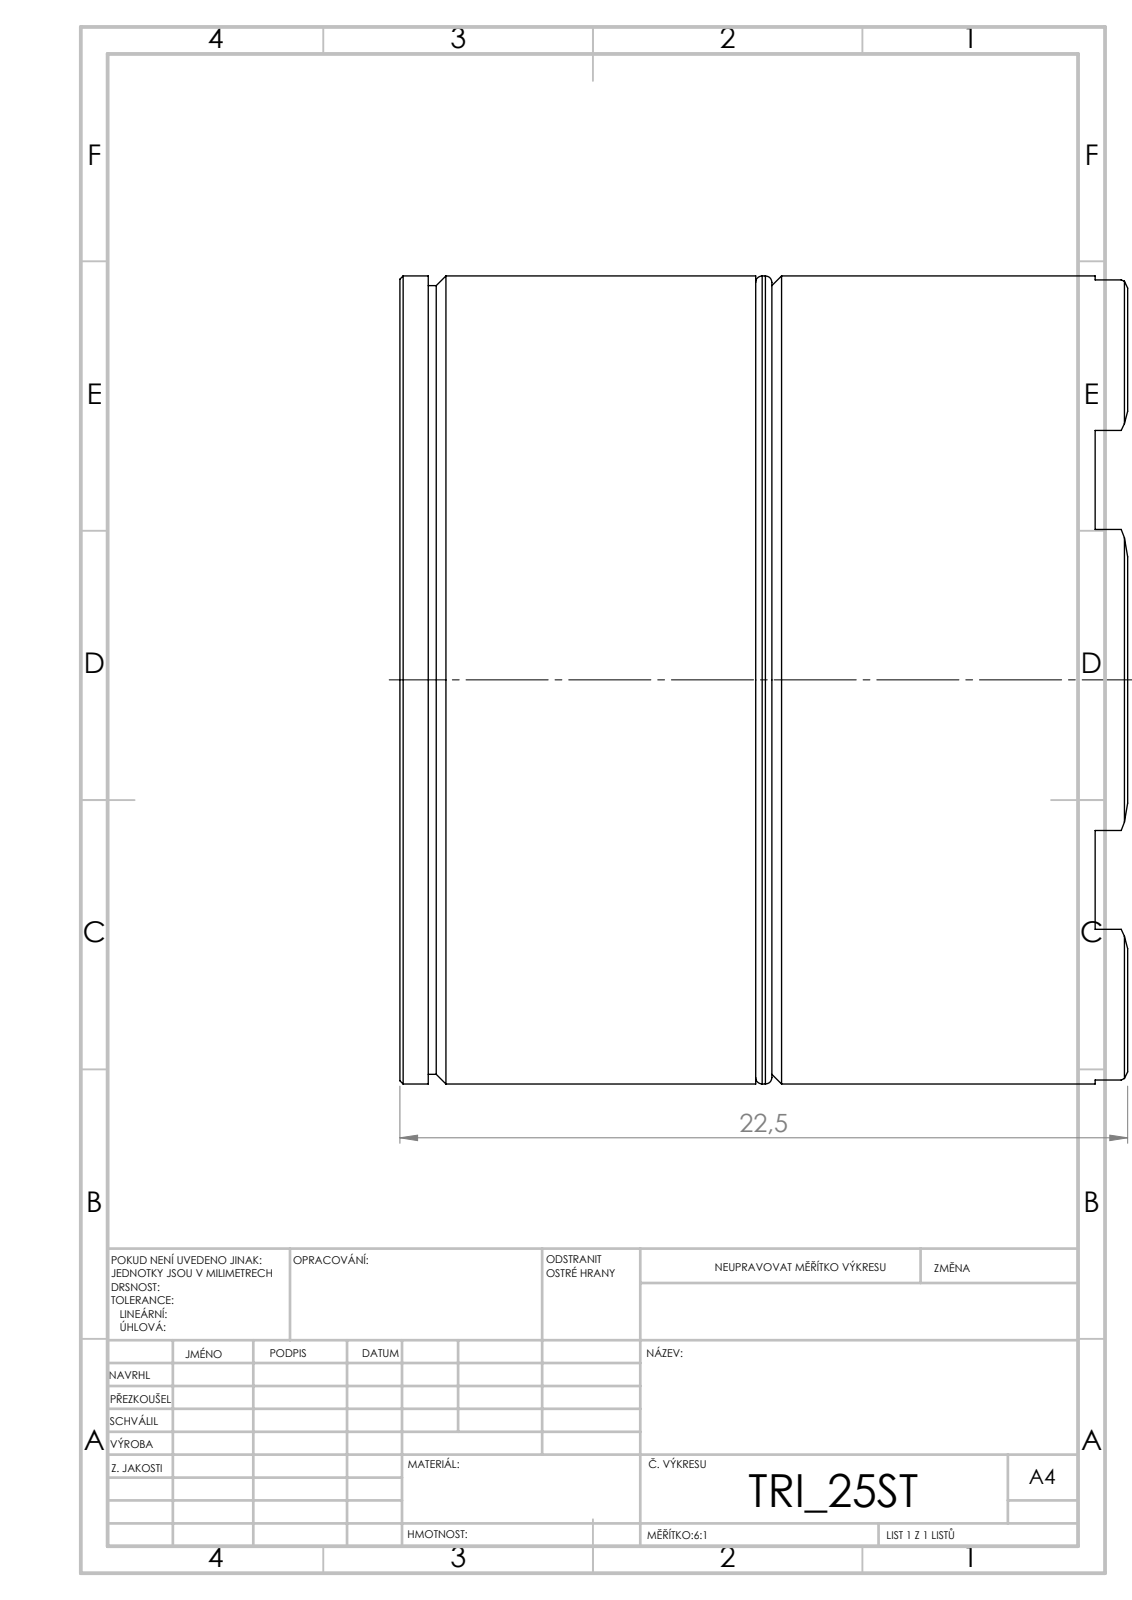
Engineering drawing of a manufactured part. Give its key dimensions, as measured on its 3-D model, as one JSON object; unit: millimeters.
{"step_written_by": "SolidWorks 2019 (CONFIG_CONTROL_DESIGN)", "units": "millimeters", "bodies": {"solids": 2, "faces": 53, "planar": 24, "cylindrical": 12, "other": 17}, "overall_size": [25, 25, 22.5], "volume_mm3": 10805, "surface_area_mm2": 3840, "round_bosses_or_shafts": [[25, 1], [24.4, 1]], "face_to_face_distances": [11, 11.5, 0.5, 10, 10.5, 21.5, 20.63, 10.63, 10.13, 0.87]}
